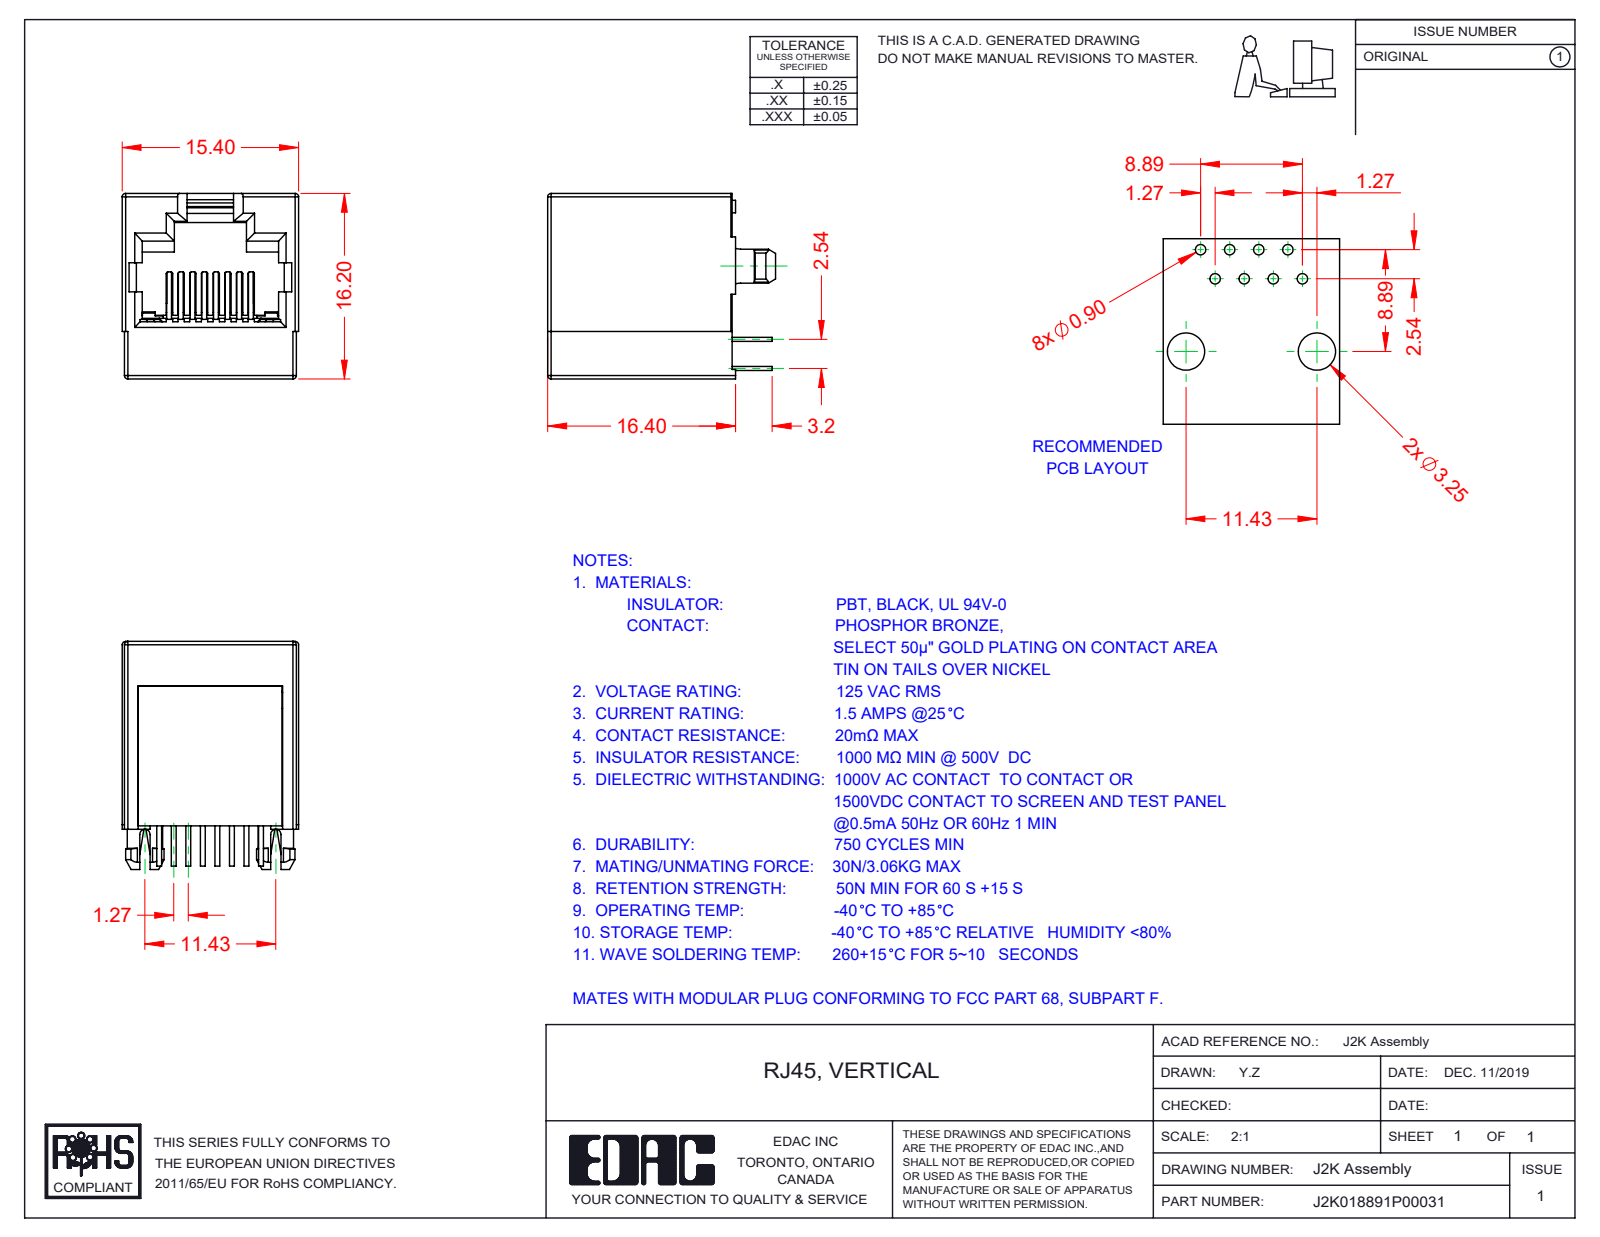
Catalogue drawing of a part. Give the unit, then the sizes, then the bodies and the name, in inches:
Units: inches
Overall size (bounding box): 0.783 × 0.638 × 0.606
Round bosses / shafts (diameter × count): ⌀0.122 ×2, ⌀0.043 ×2
Partial cylindrical surfaces — rounded edges, fillets, slot ends (radius × count): R0.006 ×16, R0.012 ×10, R0.02 ×3, R0.004 ×2, R0.008 ×2, R0.018 ×2, R0.024 ×2, R0.037 ×2
Main face-to-face distances: 0.638, 0.606, 0.055, 0.551, 0.047, 0.543, 0.598, 0.014, 0.02, 0.591
Volume: 0.151 in³ · Surface area: 6.141 in²
Bodies: 10 solids, 723 faces (586 planar, 113 cylindrical, 24 other)
Part name (STEP PRODUCT): 2K Contacts; RJ2K018891P00031; 2K Insulator; 2K Contact Lock
STEP written by: SolidWorks 2016 (CONFIG_CONTROL_DESIGN)
